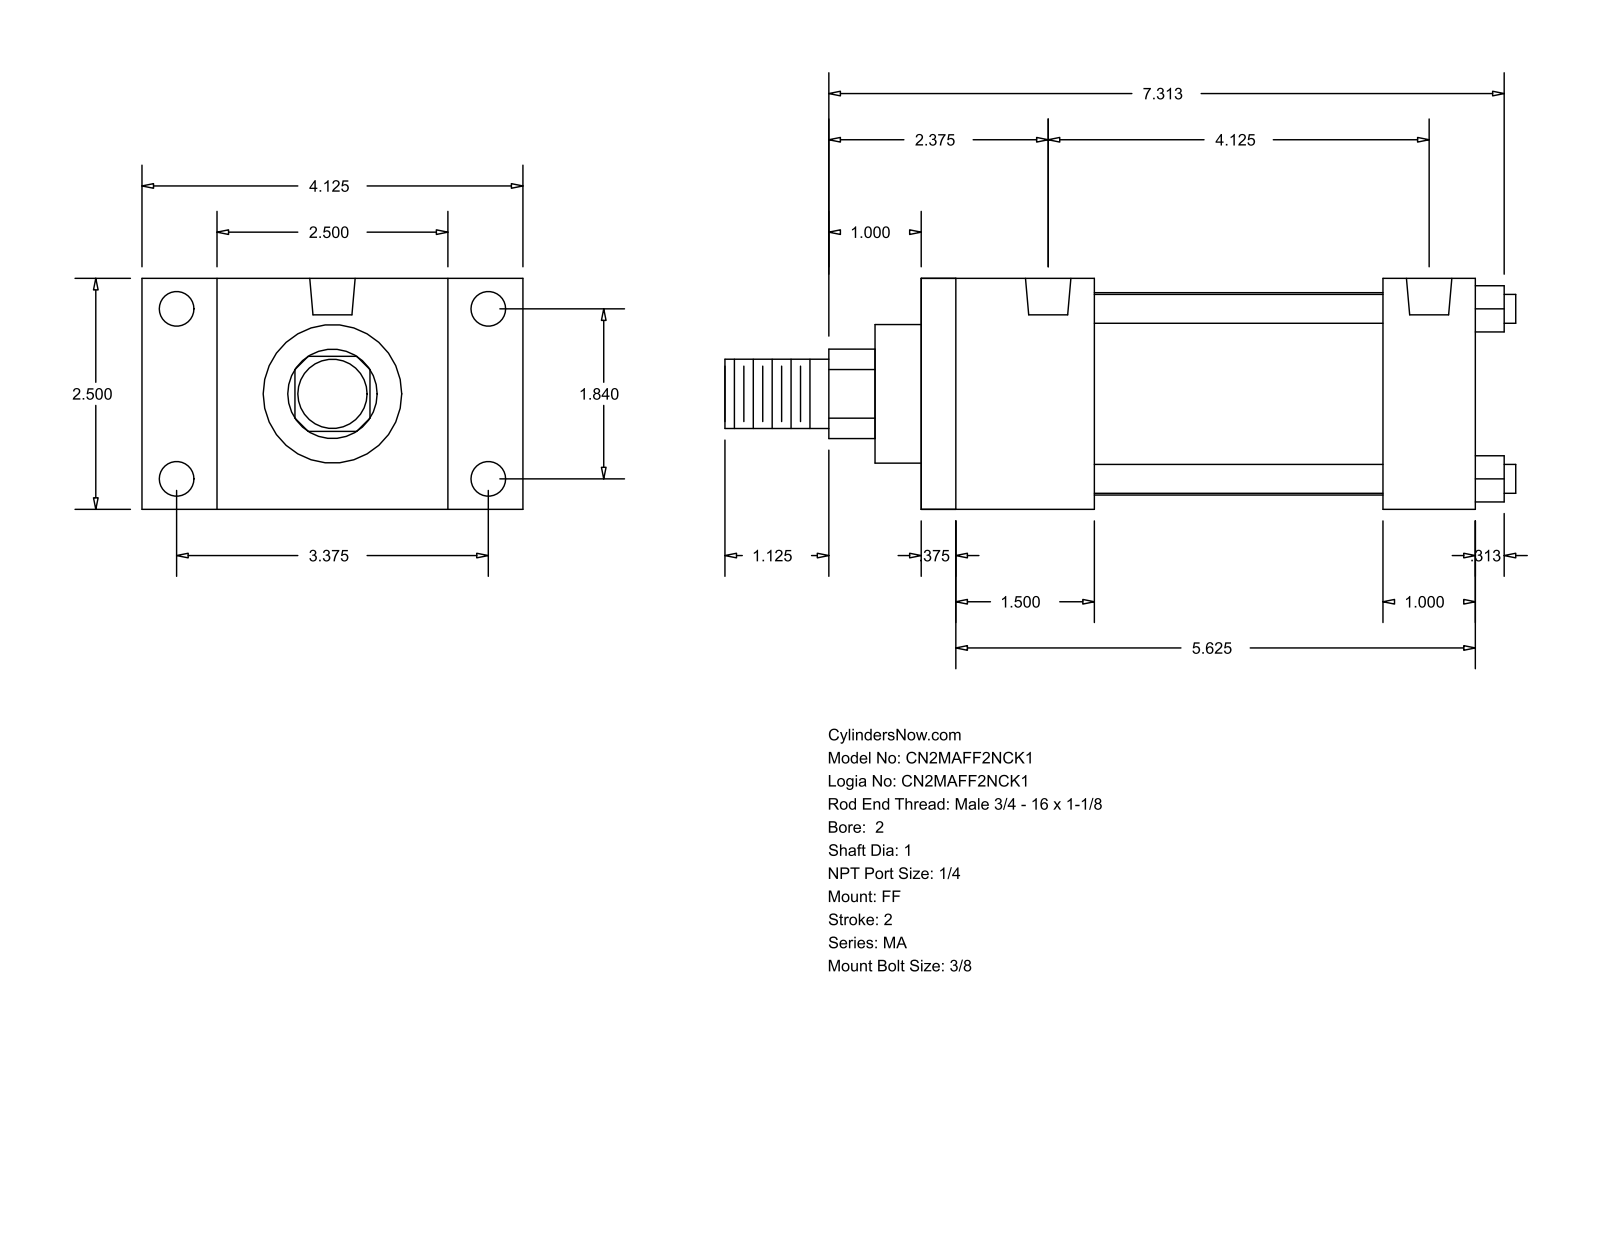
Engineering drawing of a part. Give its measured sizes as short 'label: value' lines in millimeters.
name: MA_FF__0200_1
written by: GSSL Pune (CONFIG_CONTROL_DESIGN)
unit: mm
bodies: 0 solids, 92 faces (64 planar, 28 cylindrical, 0 other)
size: 217.49 × 104.78 × 63.5
holes: 4× ⌀7.94, 4× ⌀9.53, 2× ⌀12.49
bosses: 4× ⌀7.94, 1× ⌀55.63, 1× ⌀38.1, 1× ⌀25.4, 1× ⌀19.05
rounds: 1× R12.29
face distances: 63.5, 152.4, 9.52, 142.88, 25.4, 20.64, 12.7, 47.63, 127, 38.11
hole spacings: 46.74, 85.72, 97.63, 104.77
